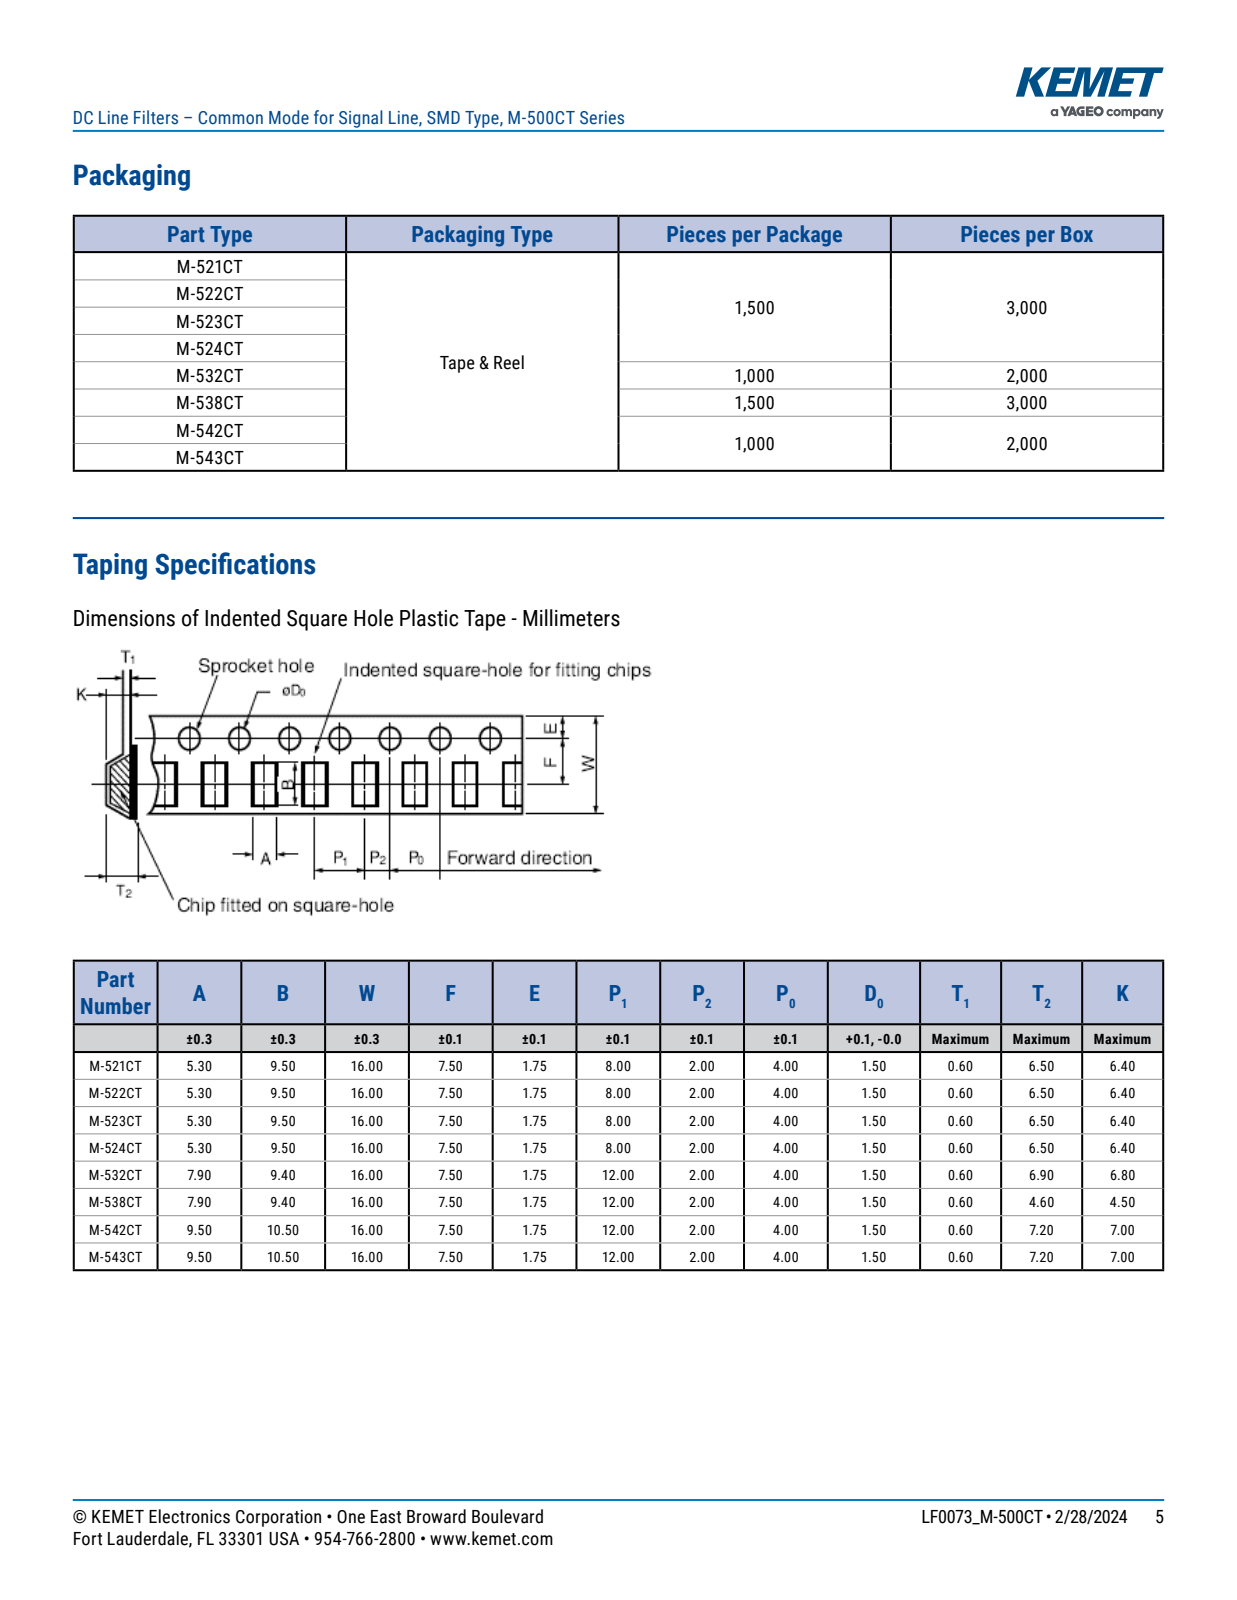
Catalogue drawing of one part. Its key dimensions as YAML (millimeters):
part_name: "IFC_NT532CT_L9W7.5T5.6"
step_written_by: "SolidWorks 2014 (AUTOMOTIVE_DESIGN)"
units: millimeters
bodies: {solids: 1, faces: 212, planar: 166, cylindrical: 46, other: 0}
overall_size: [9, 7.5, 5.61]
volume: 218
surface_area: 273
partial_cylinders:
  - {radius: 0.1, count: 6}
  - {radius: 0.25, count: 4}
face_to_face_distances: [5.5, 5.6, 7.5, 2.54, 3.31, 2.19, 2.49, 3.01, 1.2, 5.08]
